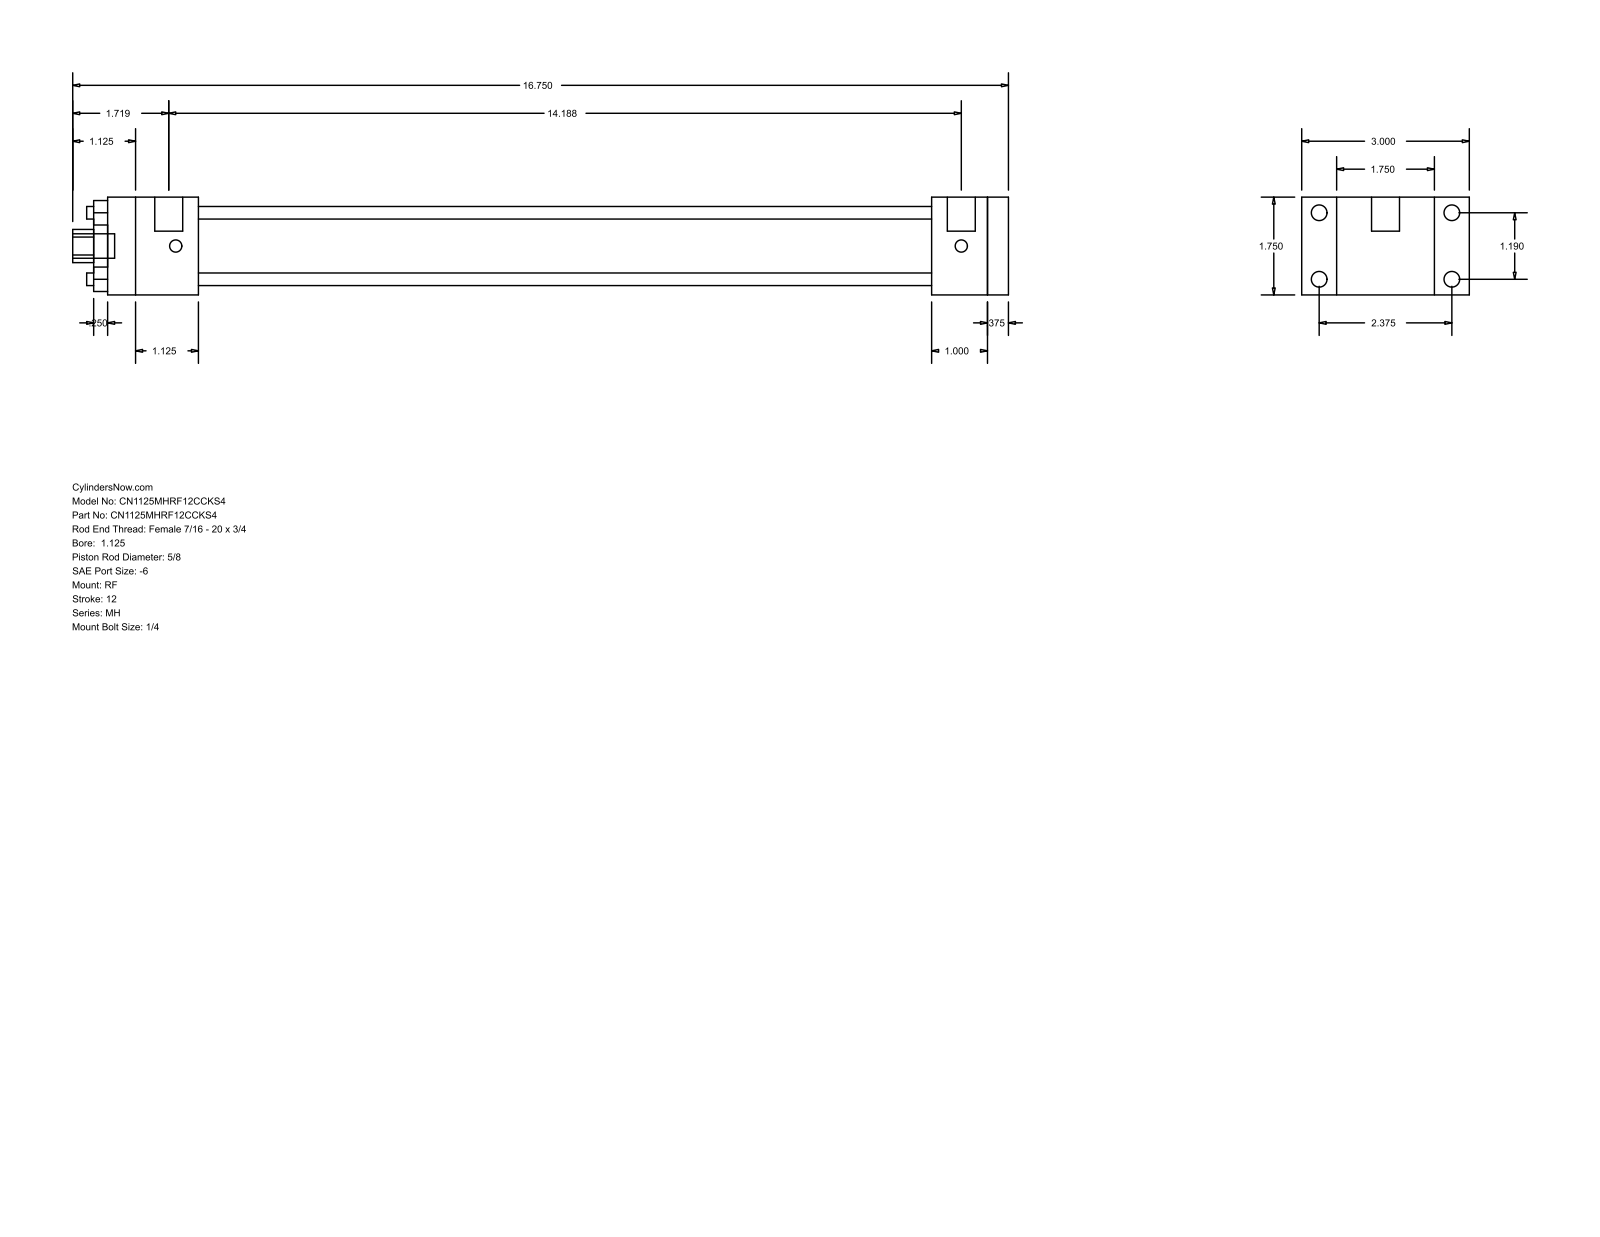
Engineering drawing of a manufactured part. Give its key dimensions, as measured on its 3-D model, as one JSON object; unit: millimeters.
{"part_name": "MH_RF__0112_0.625", "step_written_by": "GSSL Pune (CONFIG_CONTROL_DESIGN)", "units": "millimeters", "bodies": {"solids": 0, "faces": 92, "planar": 64, "cylindrical": 28, "other": 0}, "overall_size": [425.45, 76.2, 44.45], "round_holes": [[5.71, 4], [15.88, 1], [28.57, 1], [34.92, 1]], "round_bosses_or_shafts": [[7.14, 4], [5.56, 4], [12.7, 2], [11.11, 1]], "partial_cylinders_radius": [[7.54, 1]], "face_to_face_distances": [44.46, 9.52, 15.87, 358.78, 368.3, 333.37, 25.41, 34.93, 41.27, 374.64], "hole_center_spacings": [21.37, 30.22, 42.74]}
